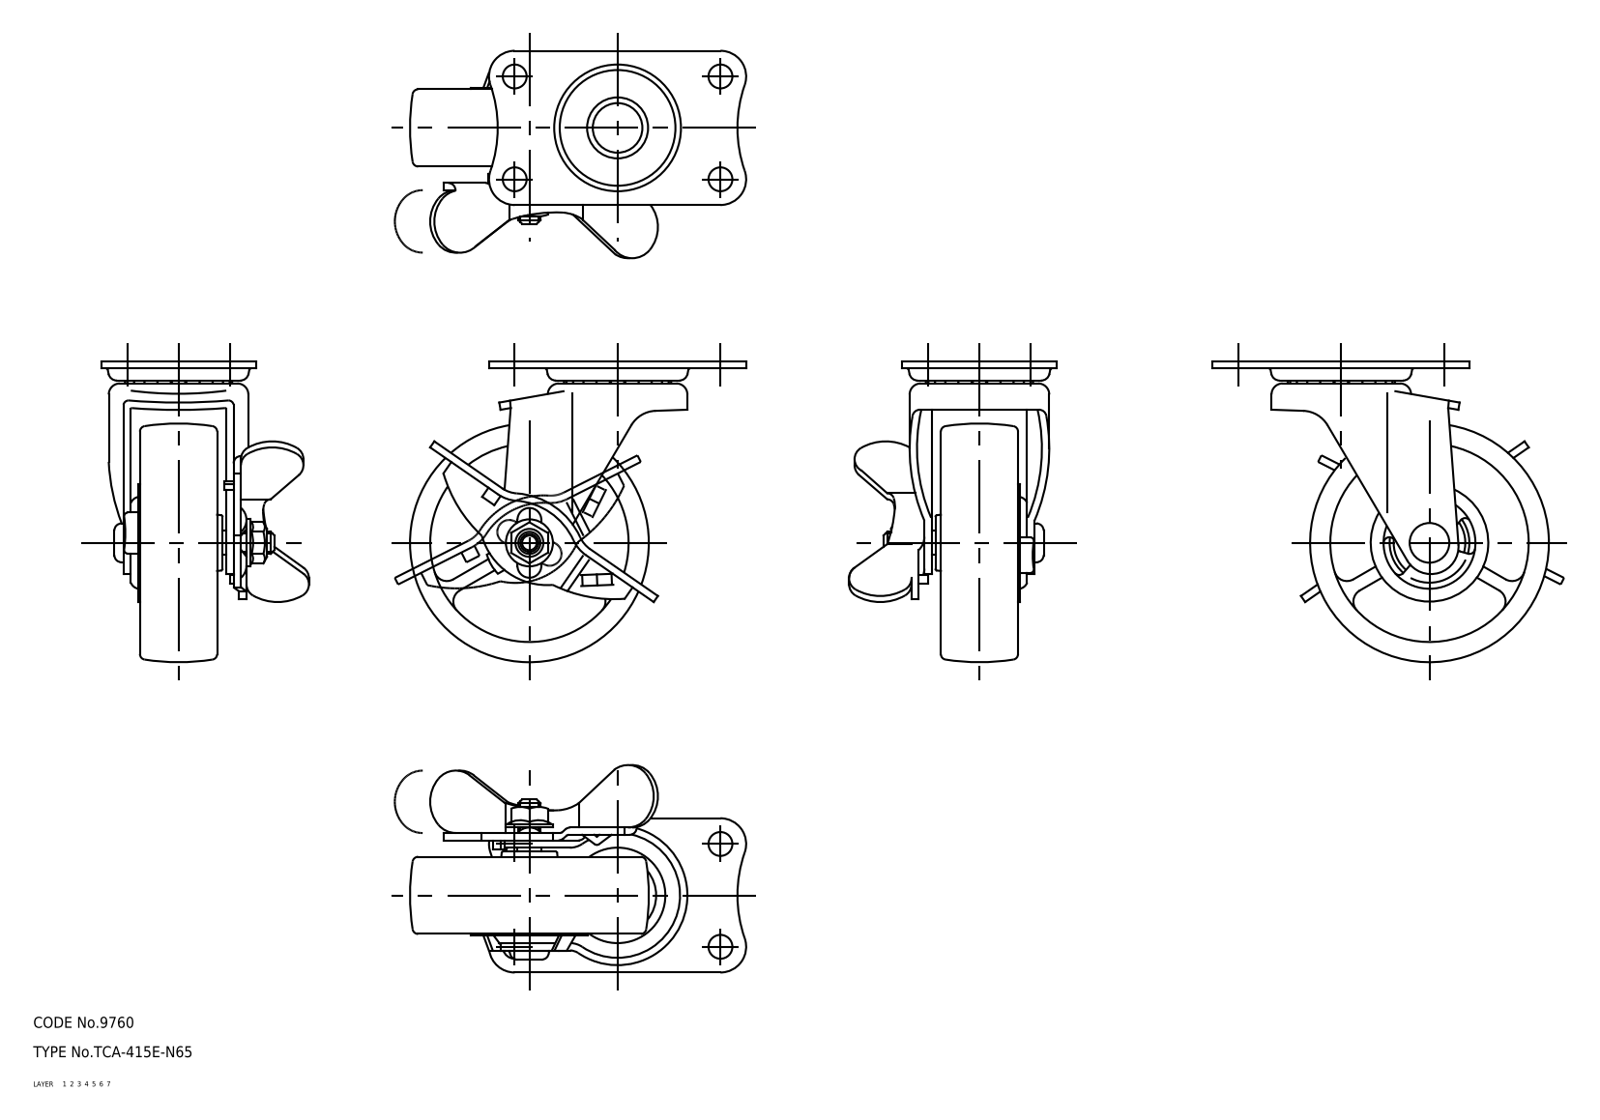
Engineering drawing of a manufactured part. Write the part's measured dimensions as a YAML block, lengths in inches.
part_name: "lever; wheel; mounting plate; main shaft (+2 more)"
step_written_by: "CADfix (AUTOMOTIVE_DESIGN)"
units: inches
bodies: {solids: 6, faces: 506, planar: 0, cylindrical: 0, other: 506}
overall_size: [3.602, 3.228, 2.224]
volume: 4.53
surface_area: 57.65
